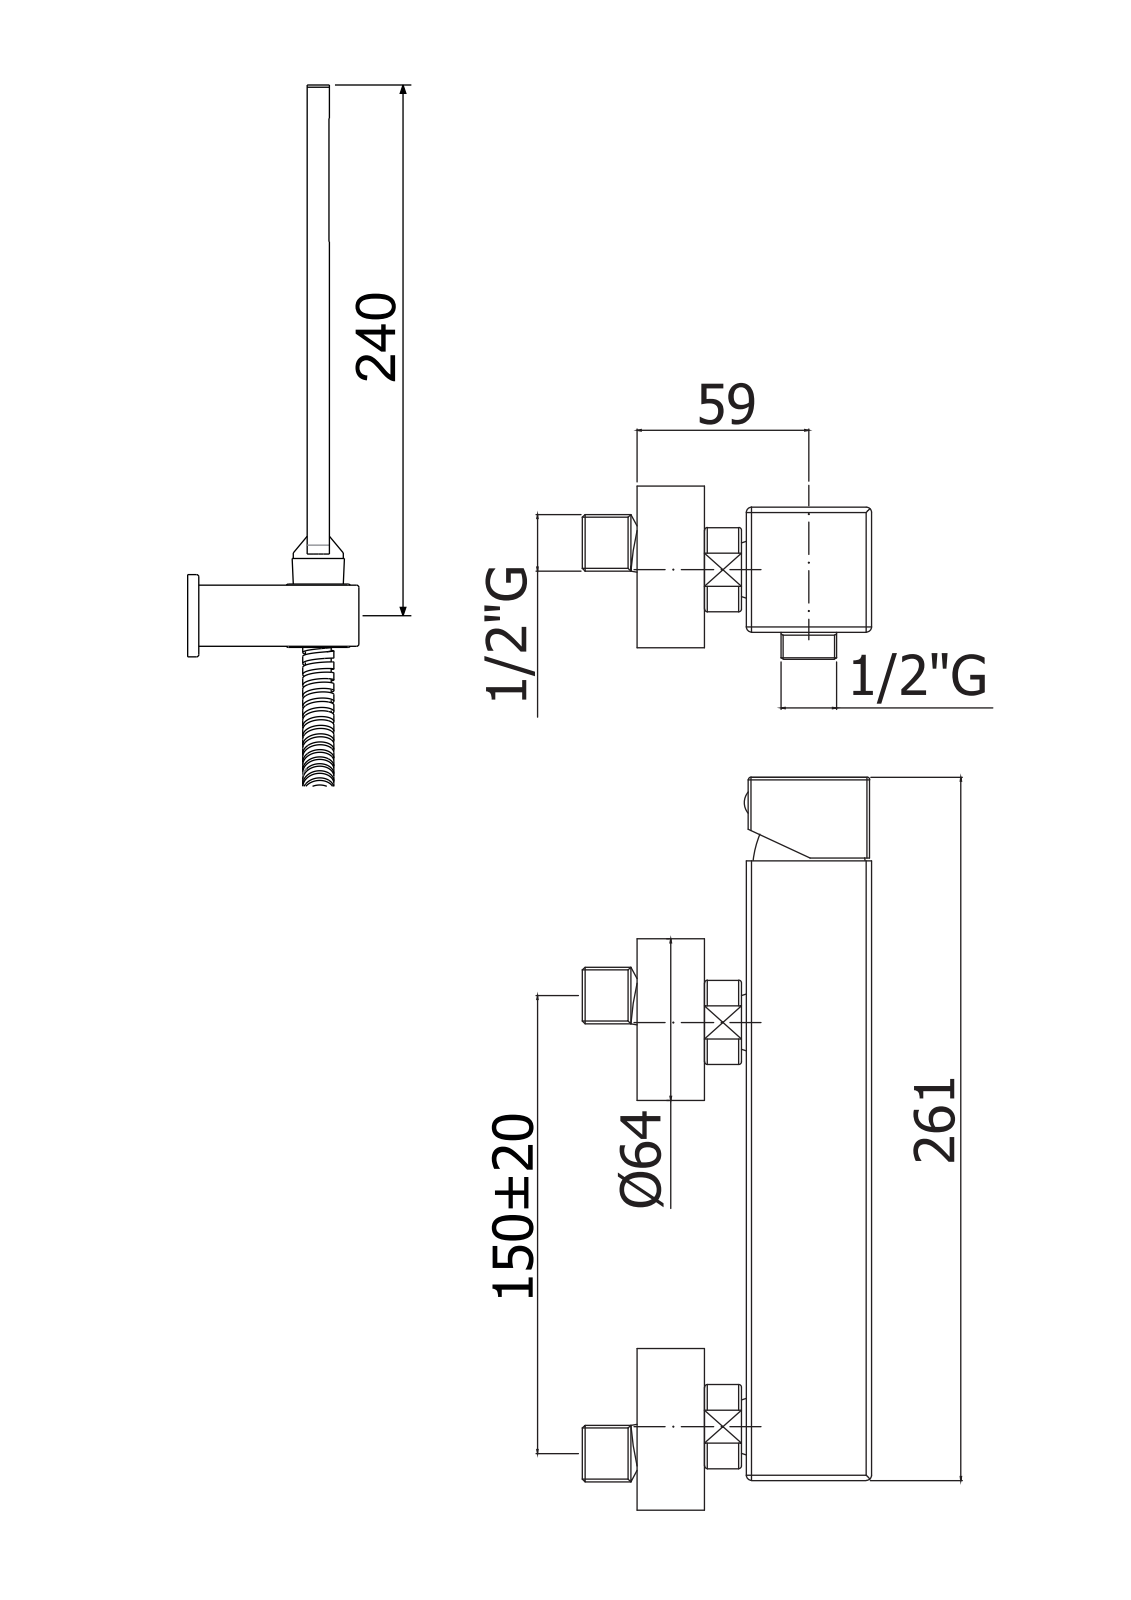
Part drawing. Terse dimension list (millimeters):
name: LEC168DCR
written by: CREO PARAMETRIC BY PTC INC, 2020044 (CONFIG_CONTROL_DESIGN)
unit: mm
bodies: 2 solids, 1951 faces (1016 planar, 526 cylindrical, 409 other)
size: 472.5 × 372 × 81.5
volume: 420 791 mm³; area: 217 976 mm²
holes: 4× ⌀12, 3× ⌀9, 2× ⌀4, 2× ⌀7, 2× ⌀8, 2× ⌀10.5, 2× ⌀18, 2× ⌀21.6, 2× ⌀24.5, 2× ⌀25, 2× ⌀37, 2× ⌀62.3
bosses: 11× ⌀2, 2× ⌀63.5, 2× ⌀27, 2× ⌀24, 2× ⌀17.7, 1× ⌀35, 1× ⌀34.8, 1× ⌀33.8
rounds: 130× R1, 50× R0.5, 11× R0.15, 9× R0.3, 4× R1.5, 4× R7, 2× R4, 2× R4.5
face distances: 3.75, 42.75, 46.5, 18.75, 39, 15, 3, 24, 27.75, 42
hole spacings: 0.71, 8.51, 8.6, 13.04, 13.21, 13.51, 6, 13
